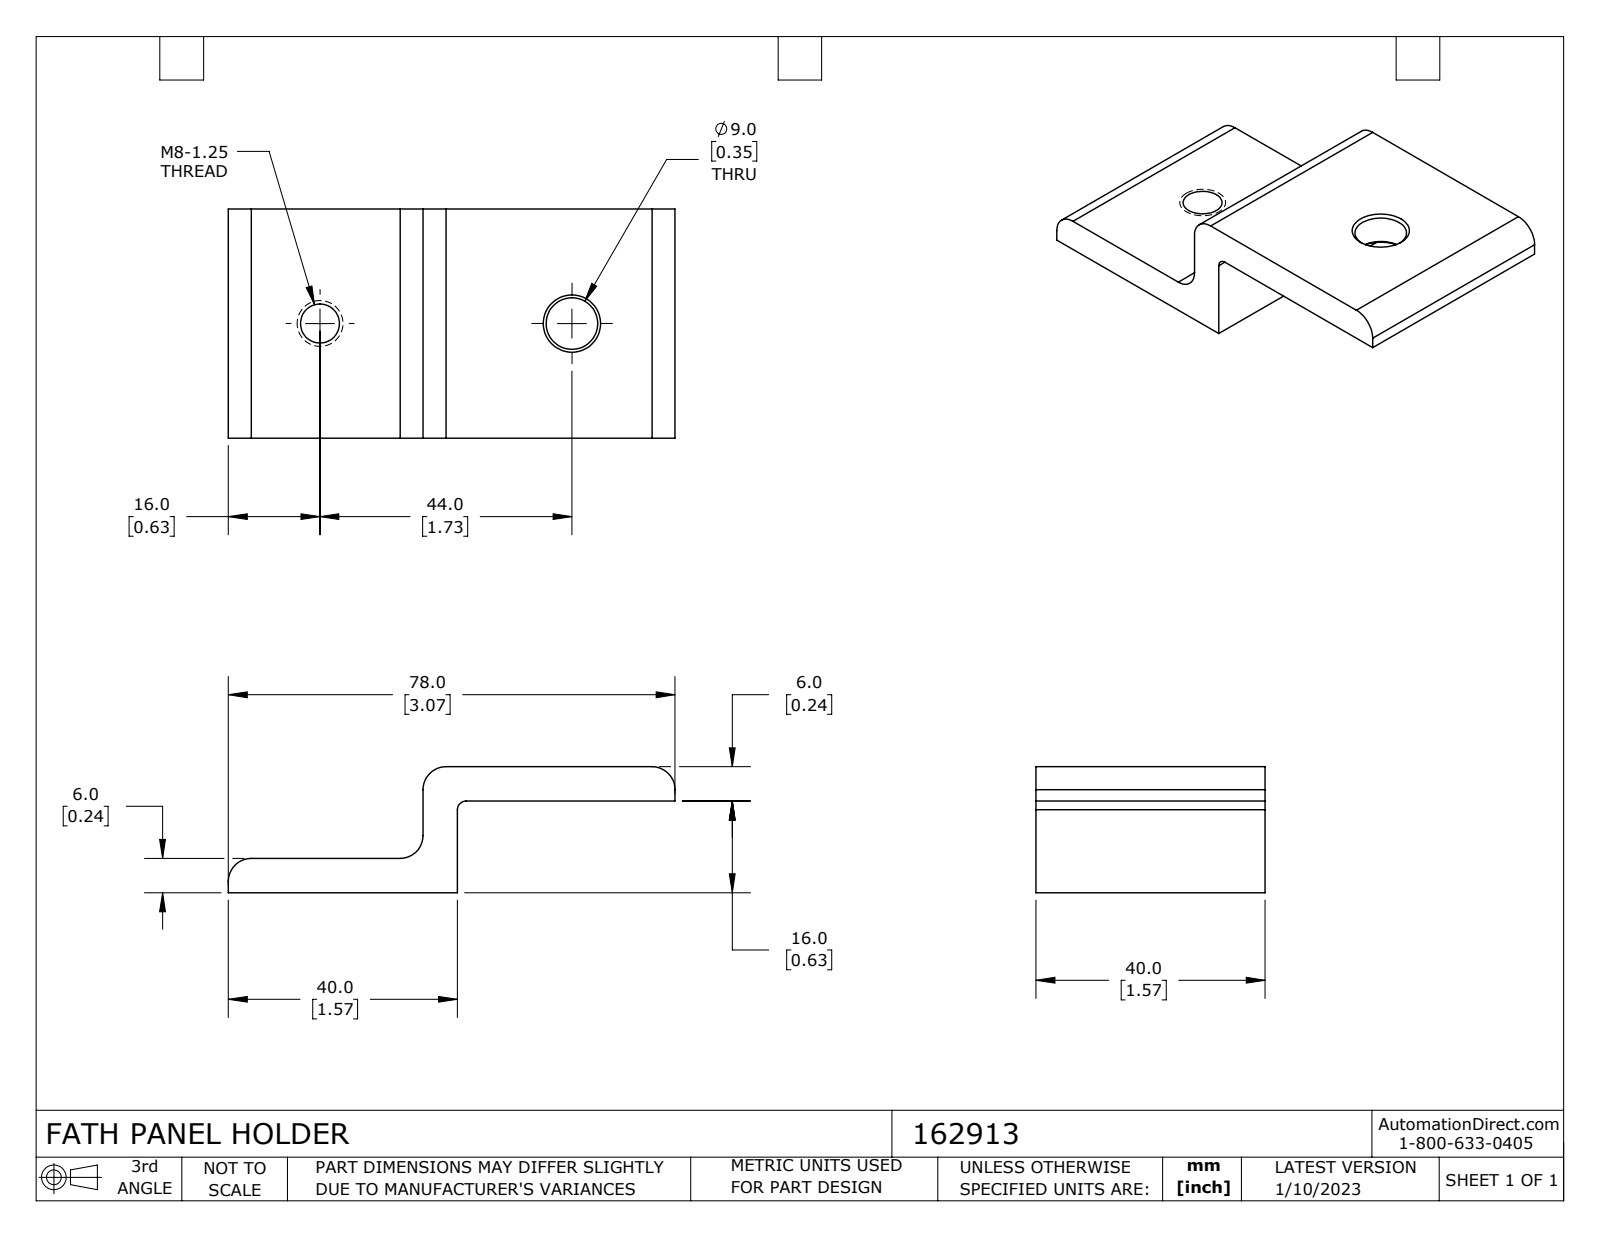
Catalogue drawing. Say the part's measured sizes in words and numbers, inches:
The part is named "162913". Its 3-D file was written by "SolidWorks 2021 (CONFIG_CONTROL_DESIGN)". It is 1 solid with 23 faces: 10 planar, 9 cylindrical and 4 other. Overall it measures 3.071 by 1.575 by 0.866 inches. Its volume is 1.324 cubic inches and its surface area 13.79 square inches. Round holes: 1 of diameter 0.268, 1 of diameter 0.354. Partial cylindrical surfaces (rounded edges, fillets, slot ends): 4 of radius 0.157, 1 of radius 0.059. The main face-to-face distances are 0.236, 0.63, 0.866, 0.394, 1.575, 1.339, 1.496, 1.732, 3.071. The hole center spacings are 1.732.
